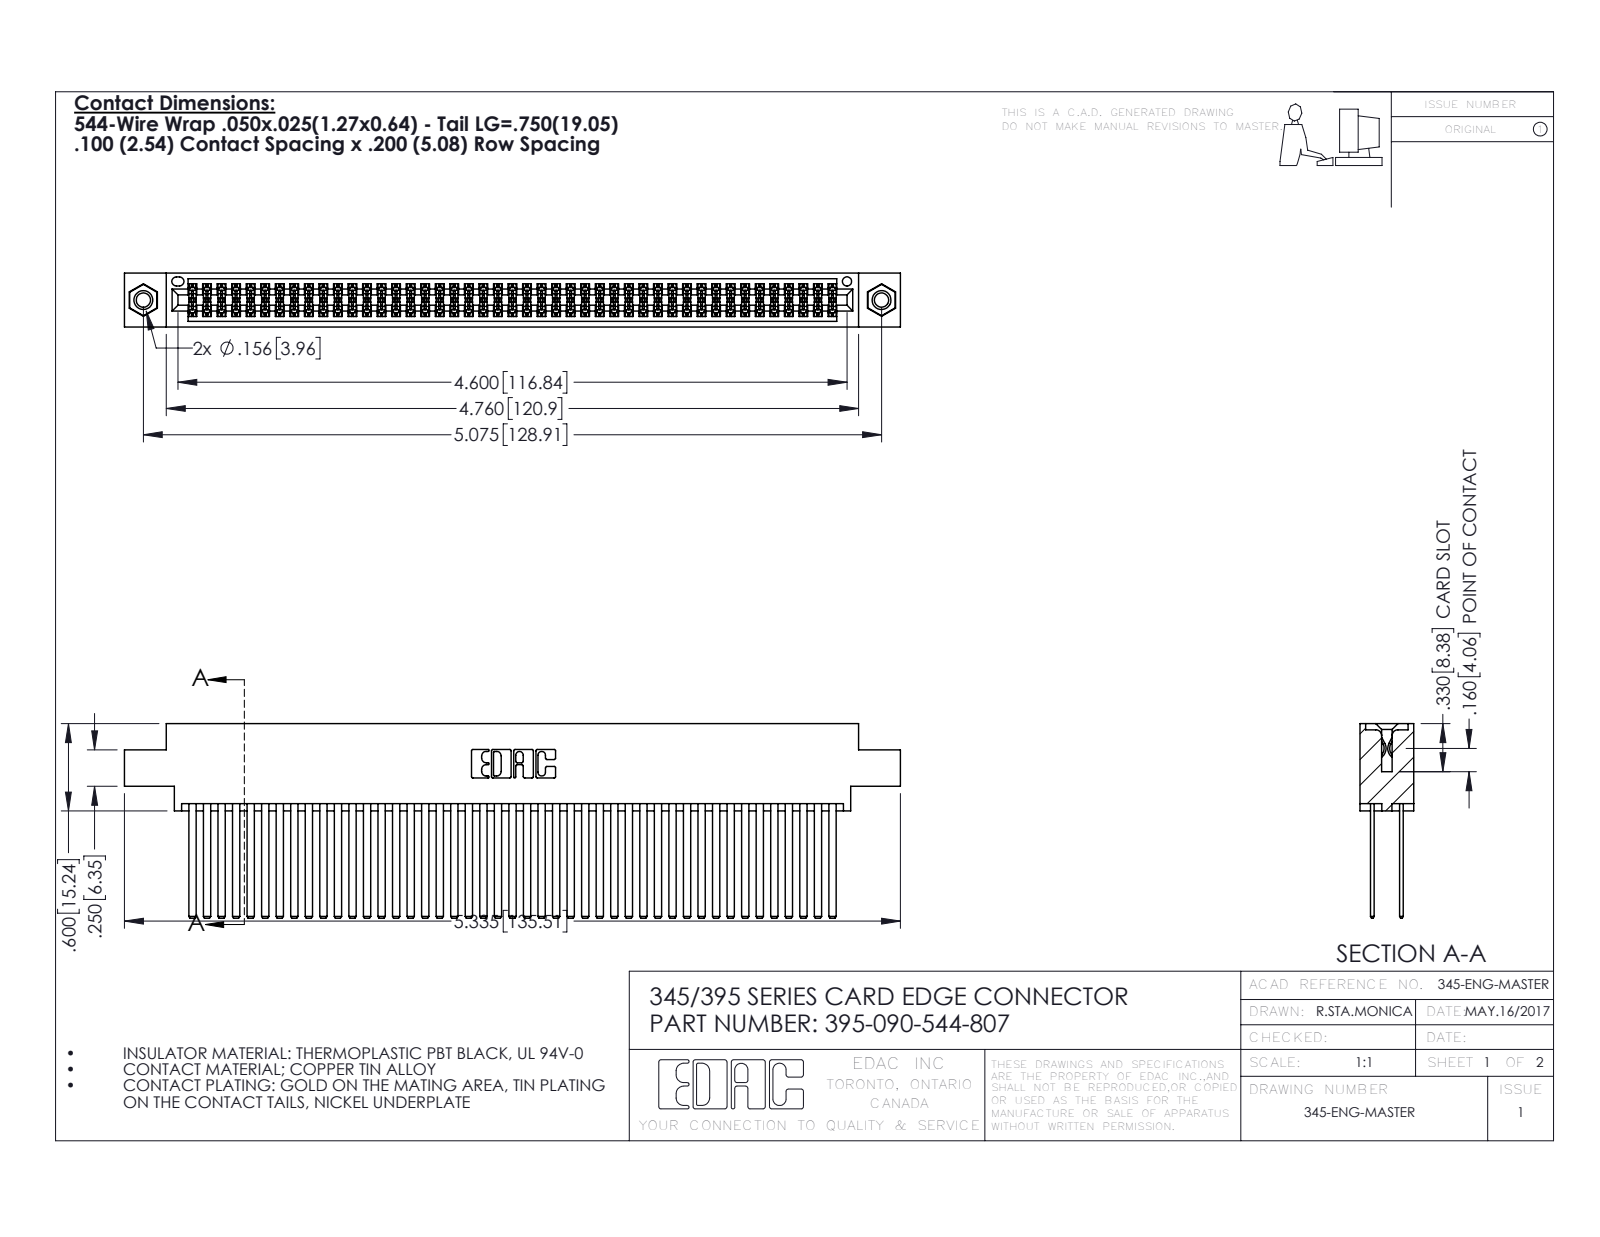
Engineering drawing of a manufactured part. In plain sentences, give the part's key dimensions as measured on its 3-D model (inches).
The part is named "345-250-001_345-250-005-103; 345-292-001_345-293-144; 345 Part_0.170 Offset - 0.156 Dia-TI; 395-090-544-807". Its 3-D file was written by "SolidWorks 2016 (CONFIG_CONTROL_DESIGN)". It is 93 solids with 4150 faces: 2726 planar, 1408 cylindrical and 16 other. Overall it measures 5.335 by 1.337 by 0.37 inches. Its volume is 0.874 cubic inches and its surface area 38.91 square inches. Round holes: 2 of diameter 0.098, 2 of diameter 0.125, 2 of diameter 0.156, 1 of diameter 0.064. Round bosses or shafts: 2 of diameter 0.155. Partial cylindrical surfaces (rounded edges, fillets, slot ends): 135 of radius 0.006, 22 of radius 0.01, 6 of radius 0.007, 6 of radius 0.031, 3 of radius 0.026, 2 of radius 0.014, 2 of radius 0.019, 2 of radius 0.022. The main face-to-face distances are 0.2, 0.025, 0.072, 0.098, 0.272, 0.298, 0.225, 0.175, 0.37, 0.15. The hole center spacings are 0.27, 4.839, 5.075.
